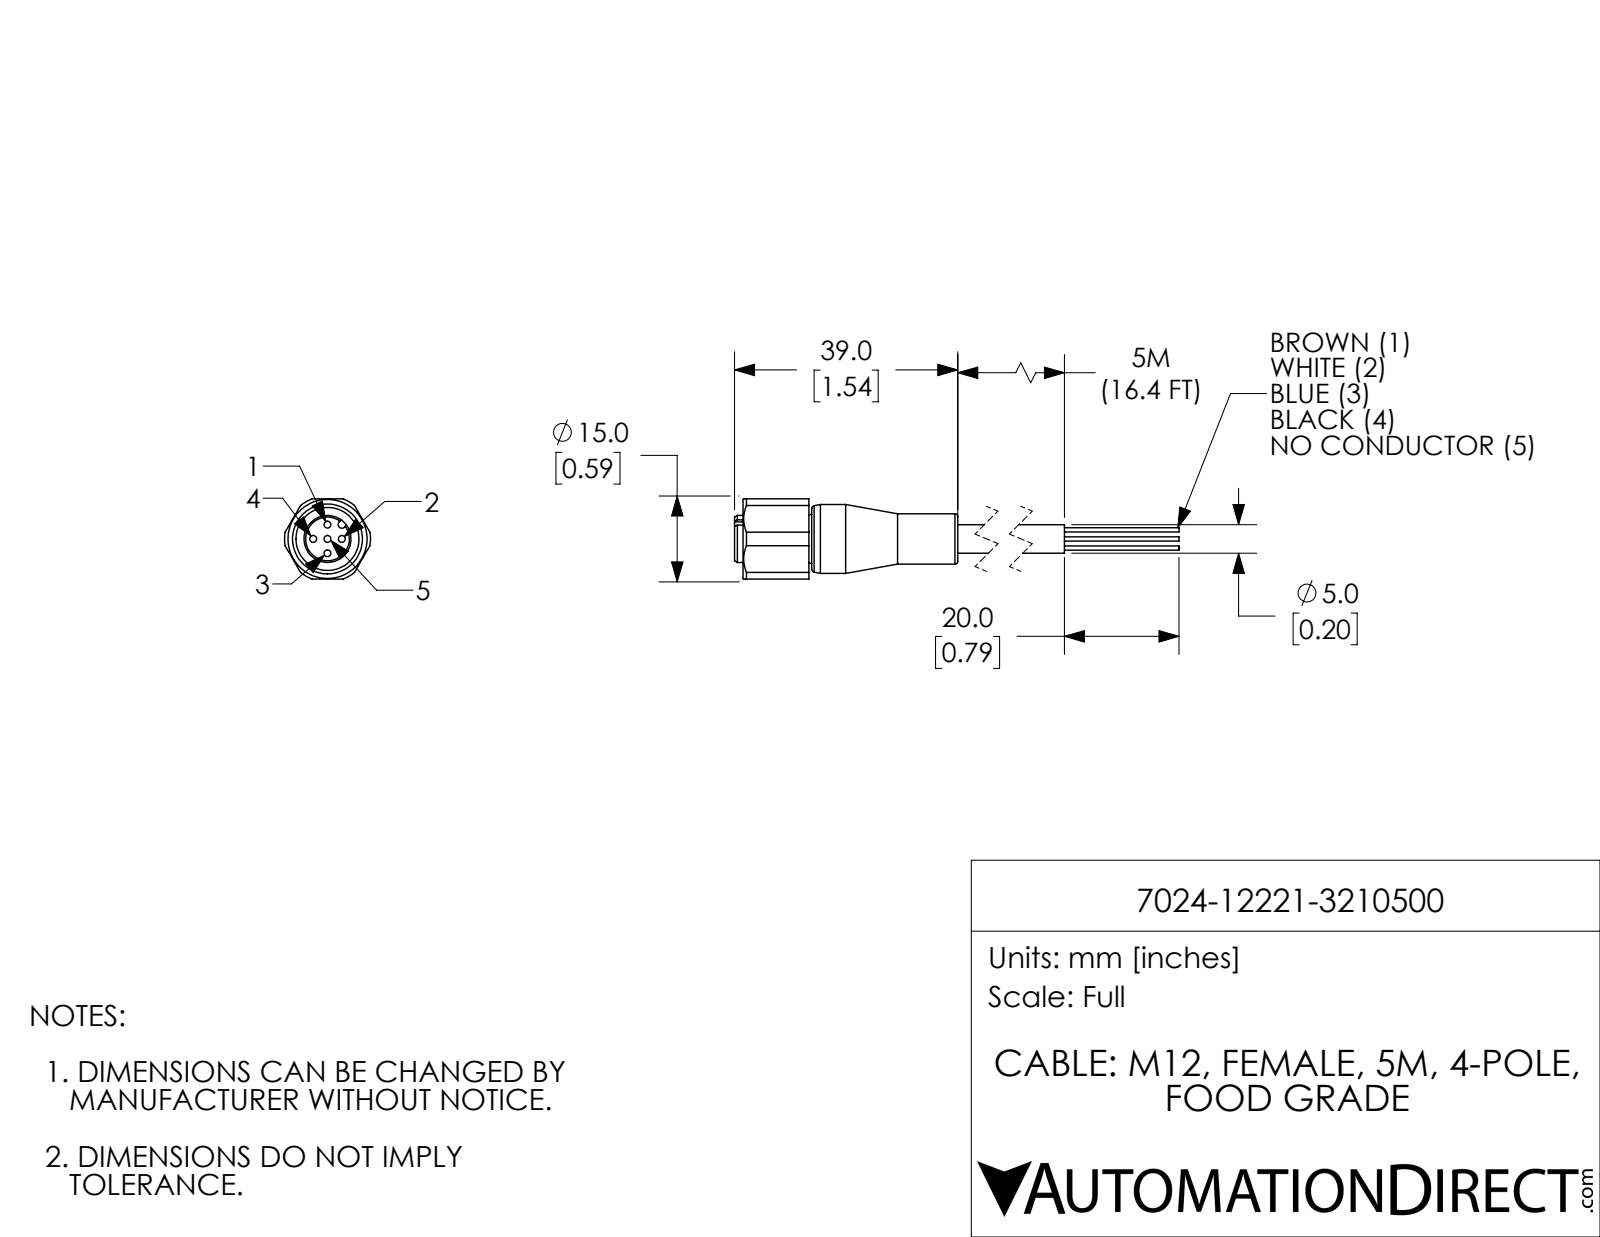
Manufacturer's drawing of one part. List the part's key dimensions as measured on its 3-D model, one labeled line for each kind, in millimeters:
Part name (STEP PRODUCT): 7024-12221-3210500
STEP written by: SolidWorks 2018 (AUTOMOTIVE_DESIGN)
Units: millimetres
Bodies: 1 solid, 77 faces (25 planar, 37 cylindrical, 15 other)
Overall size (bounding box): 77.8 × 15 × 14
Volume: 4 116 mm³ · Surface area: 2 828 mm²
Round holes (diameter × count): ⌀1.2 ×5, ⌀11 ×1
Round bosses / shafts (diameter × count): ⌀0.76 ×4, ⌀12 ×1, ⌀8.8 ×1, ⌀8.5 ×1, ⌀8.2 ×1, ⌀5 ×1
Partial cylindrical surfaces — rounded edges, fillets, slot ends (radius × count): R0.65 ×1, R7.5 ×1
Main face-to-face distances: 14, 4, 9, 13, 1.5, 7.5, 11.5, 13.5, 12, 4.5
Hole centre spacings: 2.5, 3.54, 5
